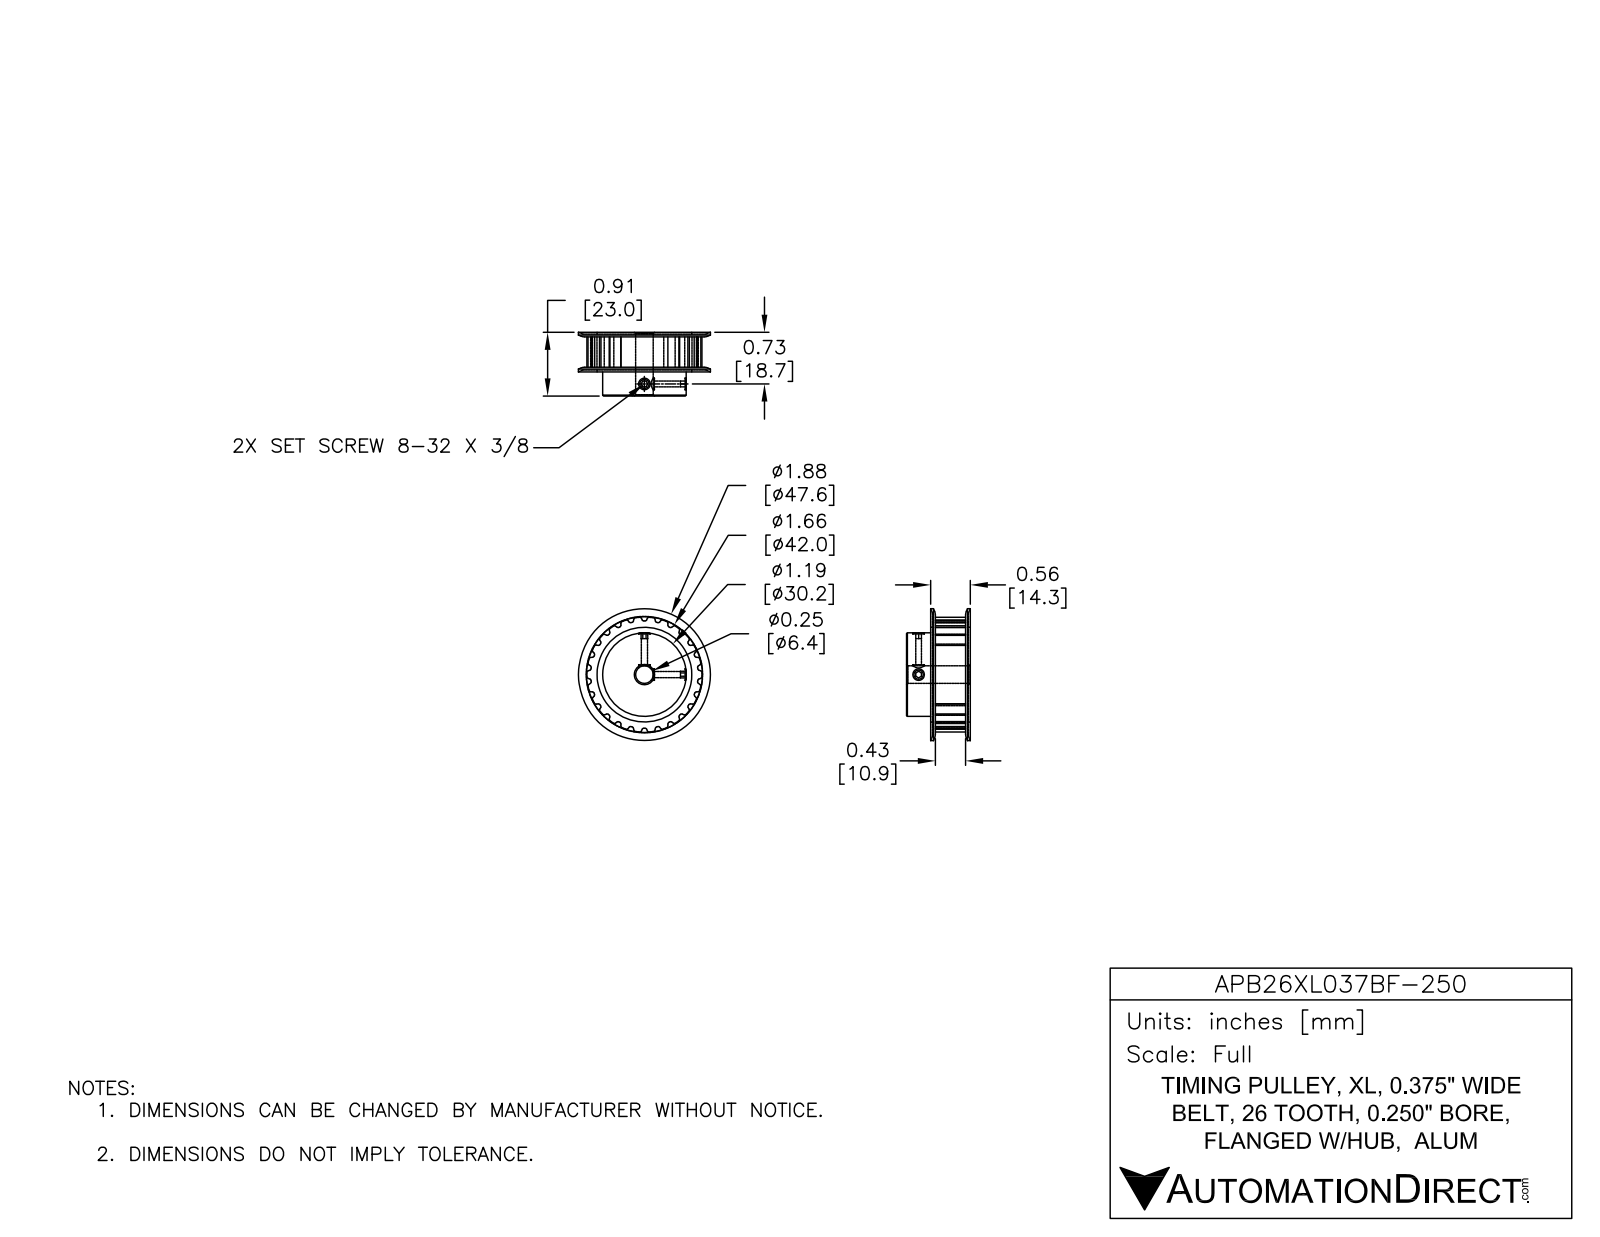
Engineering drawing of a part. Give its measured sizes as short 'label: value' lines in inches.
name: APB26XL037BF-250
written by: SolidWorks 2014 (AUTOMOTIVE_DESIGN)
unit: in
bodies: 1 solid, 265 faces (84 planar, 159 cylindrical, 22 other)
size: 1.875 × 1.875 × 0.906
volume: 1.441 in³; area: 12.64 in²
holes: 2× ⌀0.088, 1× ⌀0.25
bosses: 1× ⌀1.188
rounds: 104× R0.015, 1× R0.763
face distances: 0.033, 0.495, 0.528, 0.906, 0.873, 0.378, 0.598, 1.635, 1.635, 0.599
